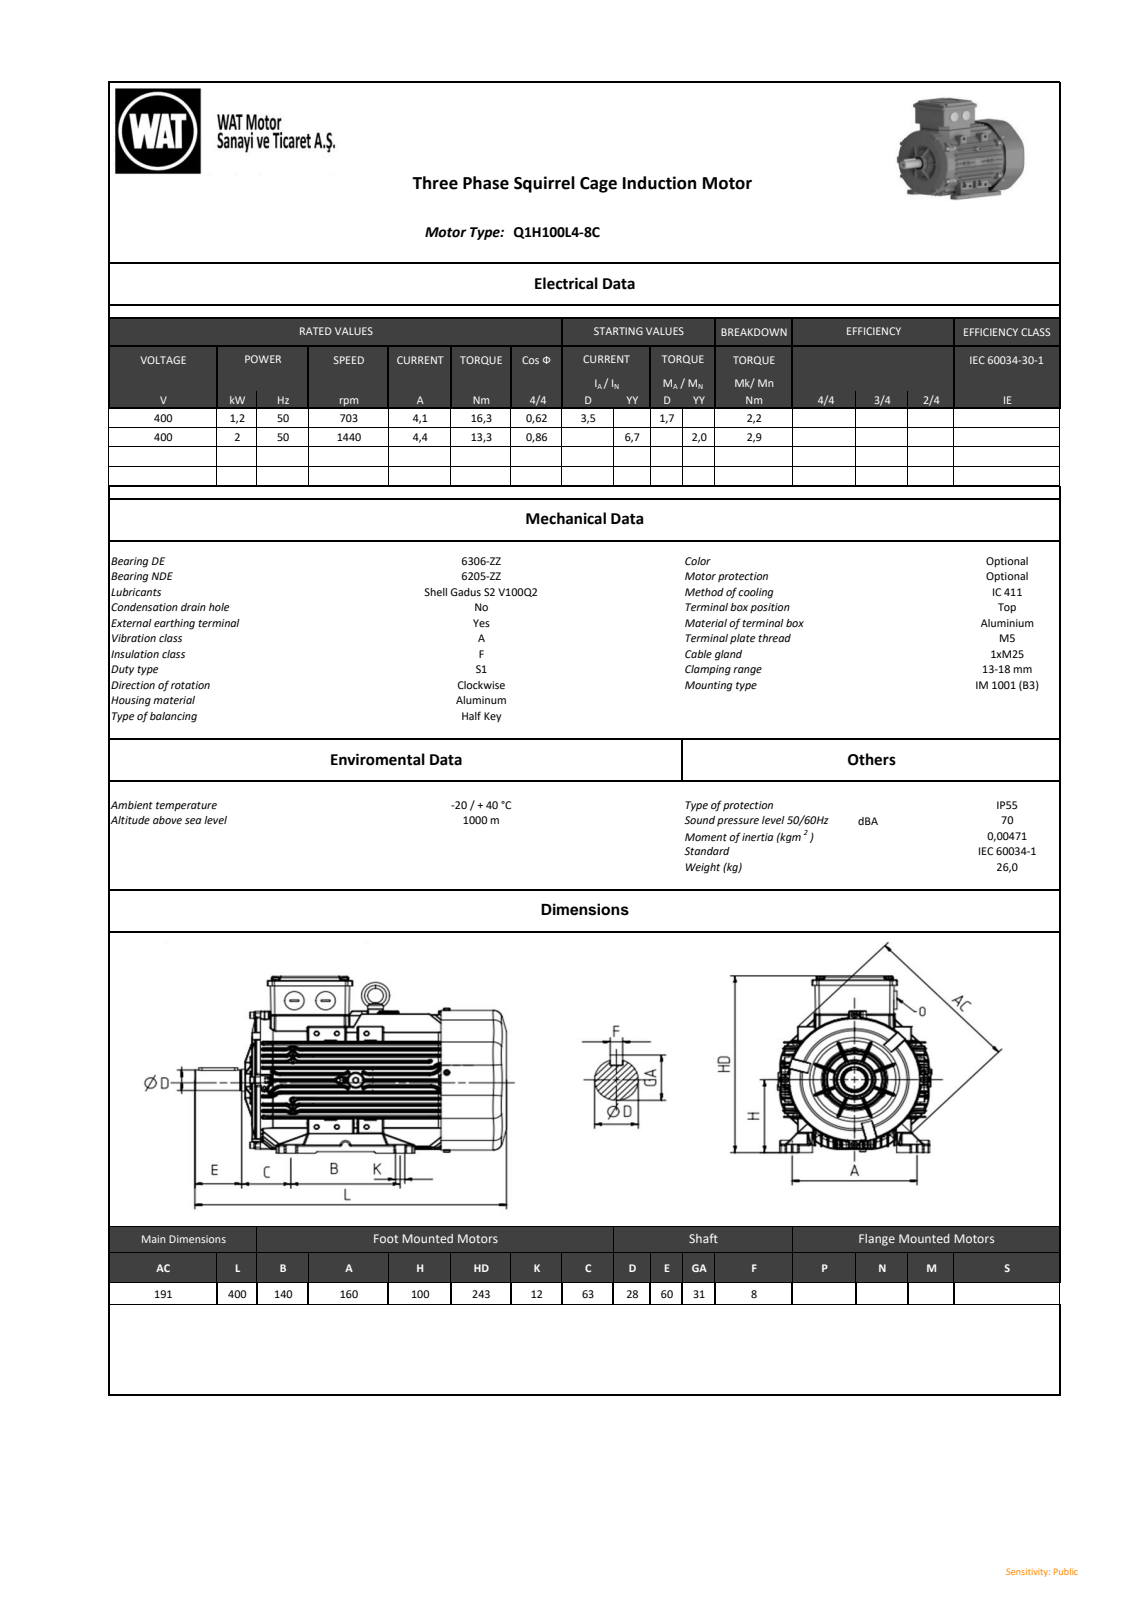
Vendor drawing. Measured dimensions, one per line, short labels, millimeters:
name: QH series_ 100_B3_stp_objects
written by: SIEMENS PLM Software NX2206.8101 (AUTOMOTIVE_DESIGN)
unit: mm
bodies: 0 solids, 5747 faces (1303 planar, 2286 cylindrical, 2158 other)
size: 399.31 × 255.72 × 197.75
holes: 4× ⌀6.5, 1× ⌀10, 1× ⌀44.42, 1× ⌀57.4, 1× ⌀89, 1× ⌀109, 1× ⌀129, 1× ⌀133
bosses: 8× ⌀8, 4× ⌀12, 4× ⌀9.3, 4× ⌀8.5, 4× ⌀5, 3× ⌀25, 1× ⌀113.5, 1× ⌀93.5
rounds: 652× R0.8, 523× R1, 129× R2, 82× R1.5, 53× R0.81, 42× R0.5, 40× R5, 26× R15
face distances: 8.53, 8.45, 8.46, 76.24, 16.91, 101.9, 25.37, 93.45, 25.58, 17.05
hole spacings: 64, 66.62, 104.41, 128, 143.11
